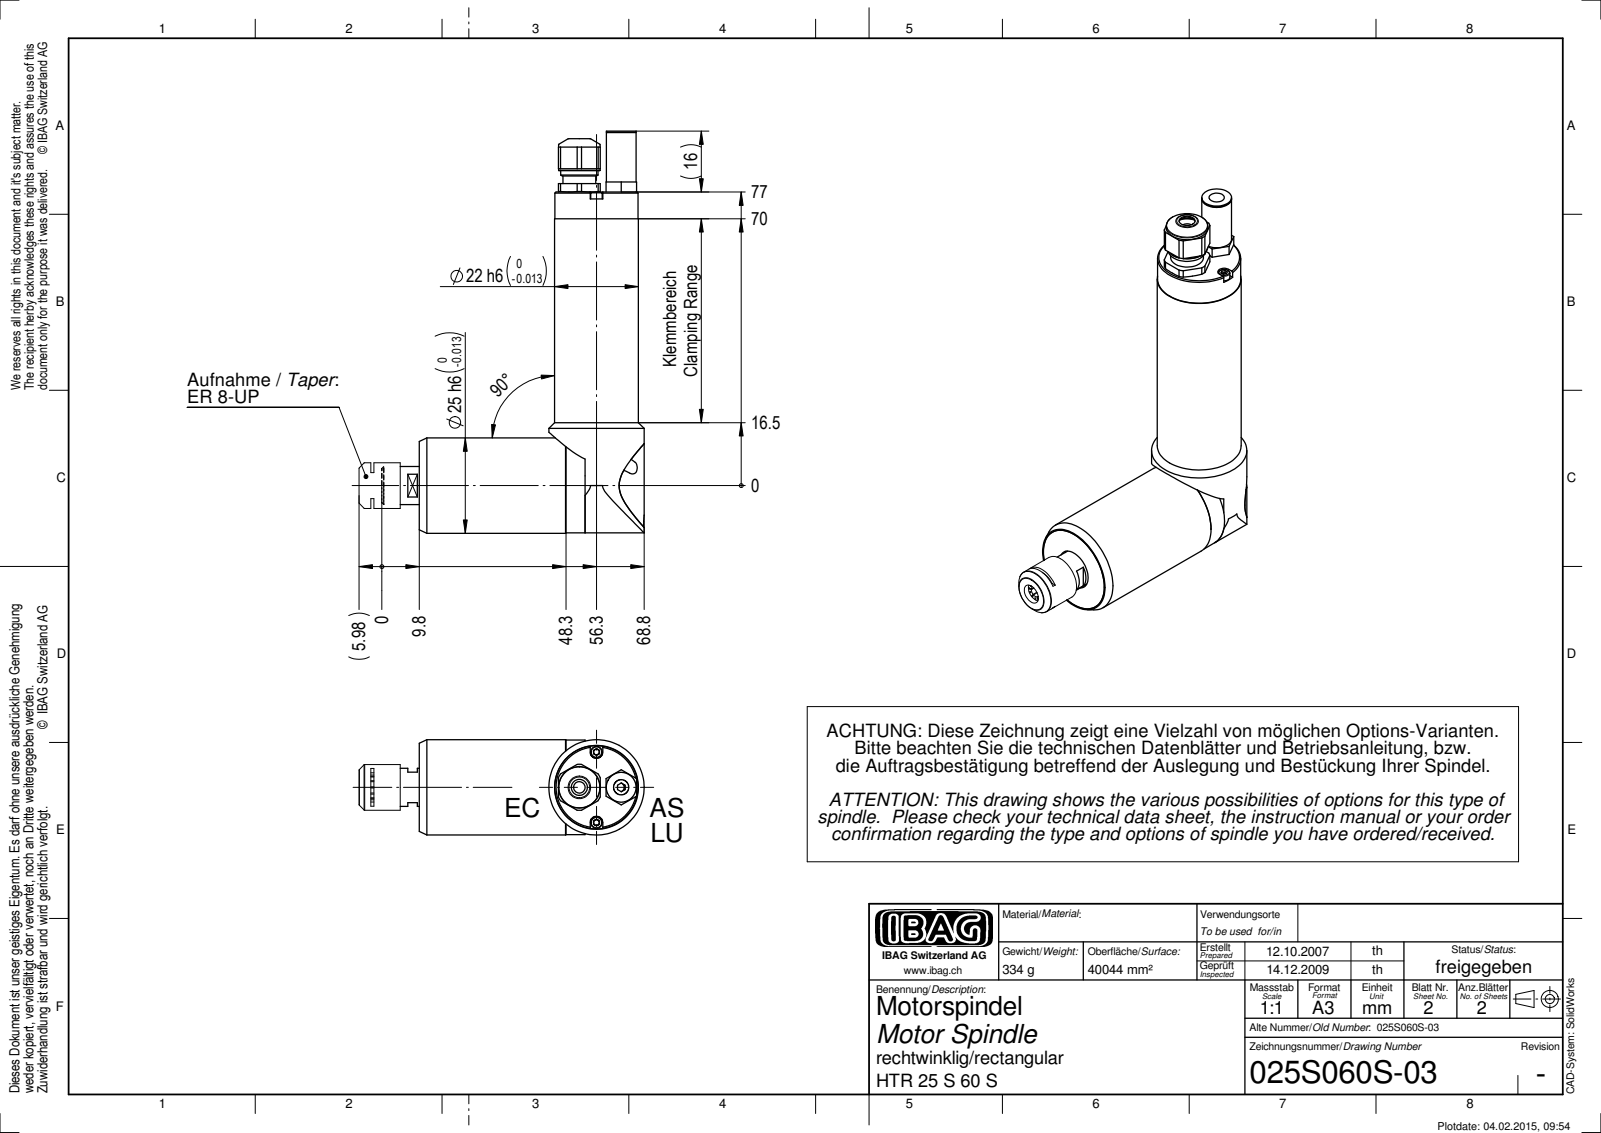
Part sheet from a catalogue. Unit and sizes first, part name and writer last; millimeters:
Units: millimetres
Overall size (bounding box): 105.5 × 74.78 × 25
Round holes (diameter × count): ⌀3 ×2, ⌀4 ×1, ⌀4.2 ×1, ⌀5.2 ×1, ⌀9.15 ×1, ⌀10.6 ×1, ⌀22 ×1, ⌀22.6 ×1
Round bosses / shafts (diameter × count): ⌀3 ×4, ⌀25 ×2, ⌀24.8 ×1, ⌀22 ×1, ⌀21.8 ×1, ⌀12 ×1, ⌀10.9 ×1, ⌀10 ×1
Partial cylindrical surfaces — rounded edges, fillets, slot ends (radius × count): R1.65 ×5, R4.25 ×1, R6.05 ×1, R14 ×1
Main face-to-face distances: 1.8, 43.5, 41.7, 7, 4, 11, 57.78, 16.08, 14.28, 1.5
Hole centre spacings: 11
Bodies: 0 solids, 236 faces (107 planar, 82 cylindrical, 47 other)
Part name (STEP PRODUCT): 025S060S-03
STEP written by: SolidWorks 2010 (CONFIG_CONTROL_DESIGN)
